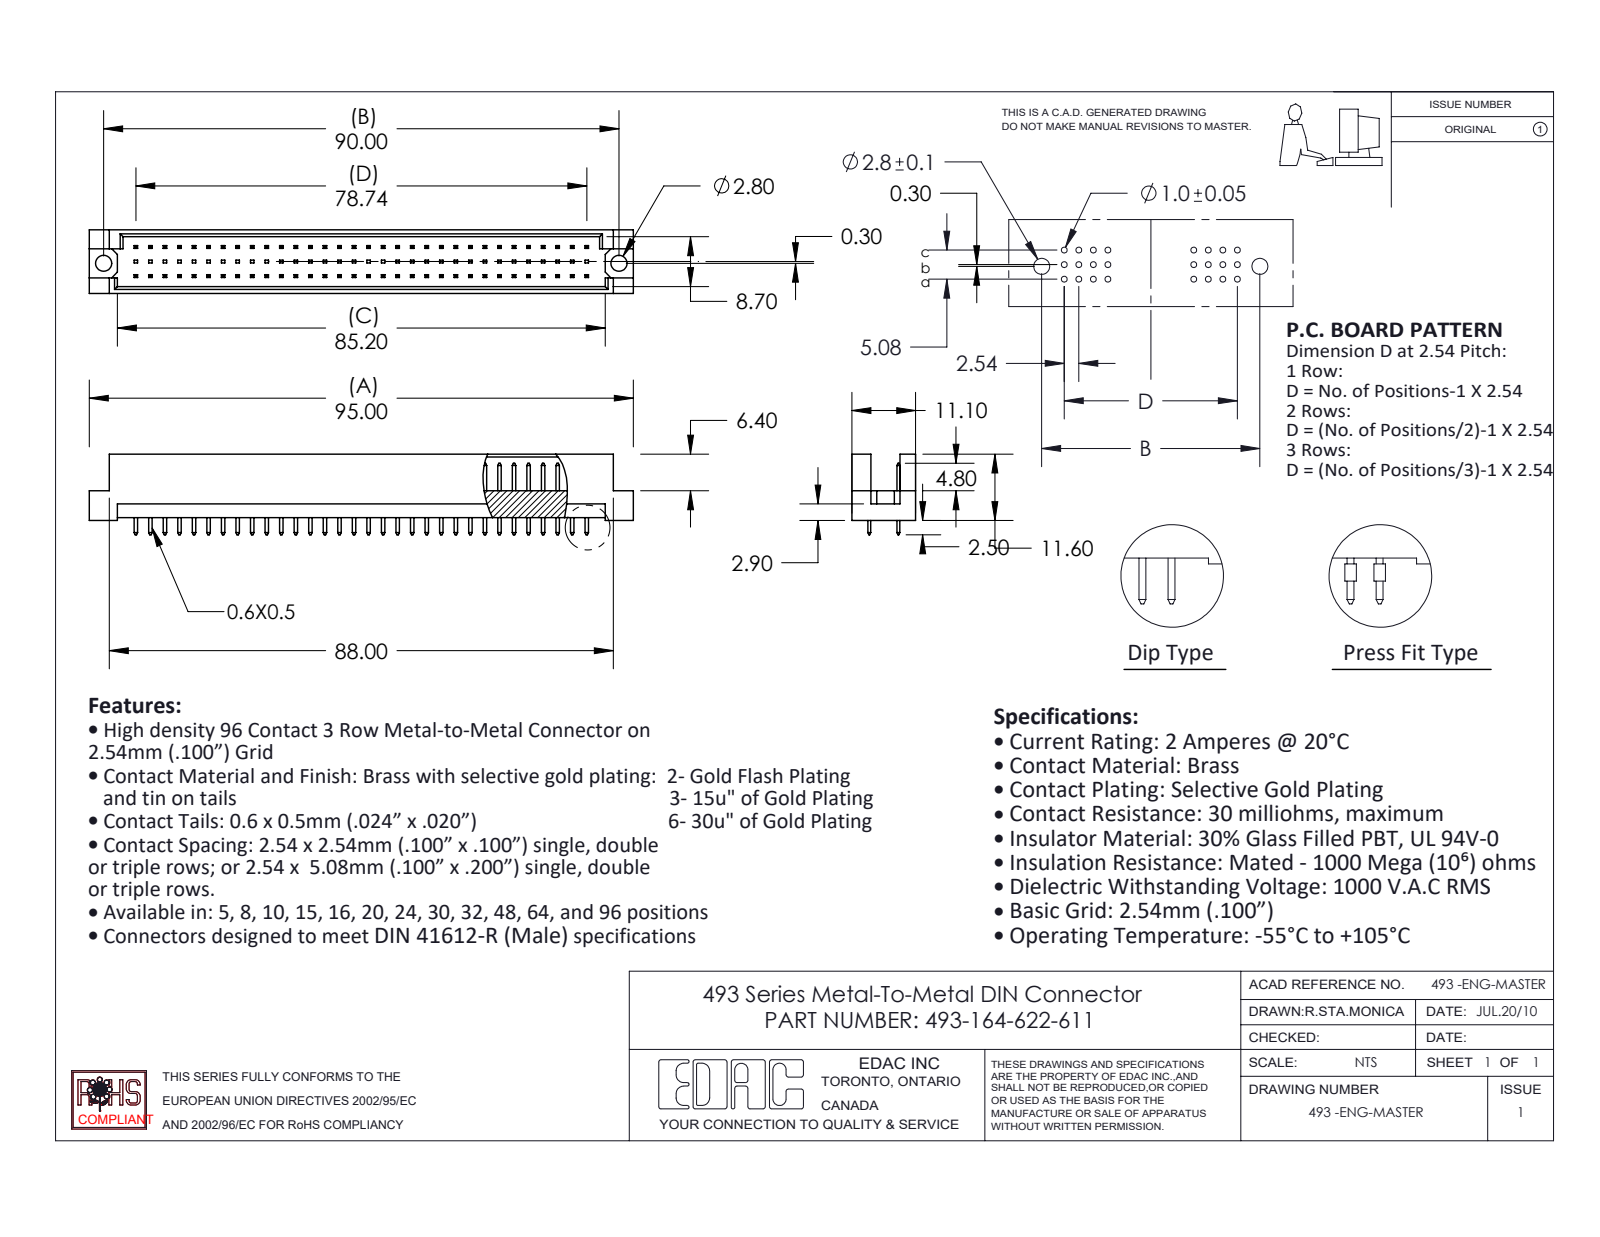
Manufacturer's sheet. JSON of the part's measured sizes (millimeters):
{"part_name": "493-164-622-611; 493-290_22; 493 Part_96", "step_written_by": "SolidWorks 2020 (CONFIG_CONTROL_DESIGN)", "units": "millimeters", "bodies": {"solids": 65, "faces": 1332, "planar": 1328, "cylindrical": 4, "other": 0}, "overall_size": [95, 14.1, 11.1], "volume_mm3": 5892, "surface_area_mm2": 8210, "round_holes": [[2.8, 2]], "face_to_face_distances": [1.2, 9.9, 11.1, 5.08, 8.7, 0.5, 4.7, 2.76, 3.26, 7.84], "hole_center_spacings": [90]}
